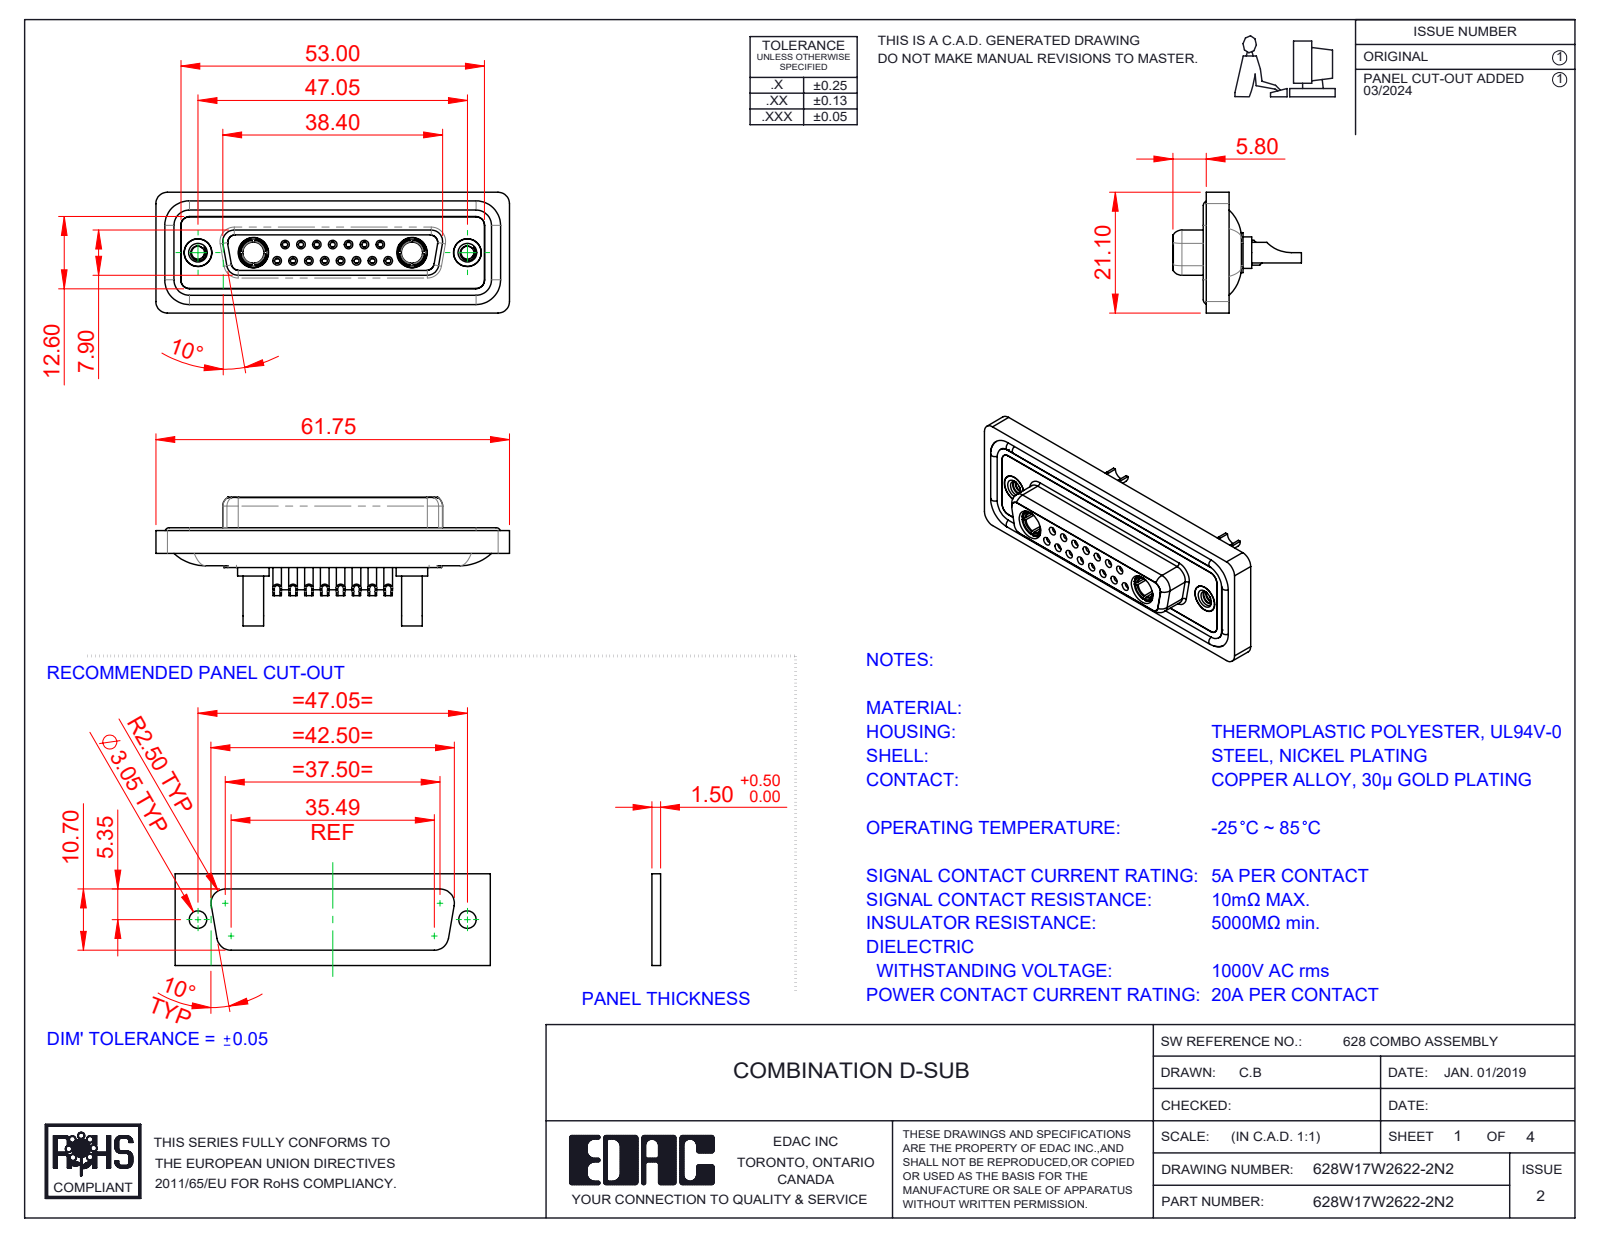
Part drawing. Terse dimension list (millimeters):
name: 628Combo Threaded Rivet_2; 628Combo Shell Rear_25 Contacts; Power Socket_20A SC; 628W17W2622-2N2 (+5 more)
written by: SolidWorks 2023 (CONFIG_CONTROL_DESIGN)
unit: mm
bodies: 26 solids, 1371 faces (424 planar, 555 cylindrical, 392 other)
size: 61.75 × 22.45 × 21.1
volume: 8 381 mm³; area: 14 180 mm²
holes: 15× ⌀0.9, 15× ⌀1, 15× ⌀1.1, 15× ⌀1.5, 15× ⌀2, 8× ⌀1.6, 7× ⌀1.7, 4× ⌀4.85, 2× ⌀2.26, 2× ⌀2.7, 2× ⌀3.7, 2× ⌀4
bosses: 15× ⌀2.2, 11× ⌀1.6, 2× ⌀5.5, 2× ⌀5.2, 2× ⌀4.96, 2× ⌀4.95, 2× ⌀4.8, 2× ⌀4.75
rounds: 22× R1.5, 18× R2, 8× R1.35, 8× R1.6, 6× R1, 4× R0.25, 4× R0.5, 4× R0.6
face distances: 0.4, 1.8, 7.45, 5.65, 6.6, 0.5, 7.05, 1.6, 2.9, 1.1
hole spacings: 3.16, 2.77, 8.31, 5.54, 5.03, 5.04, 7.49, 11.08
